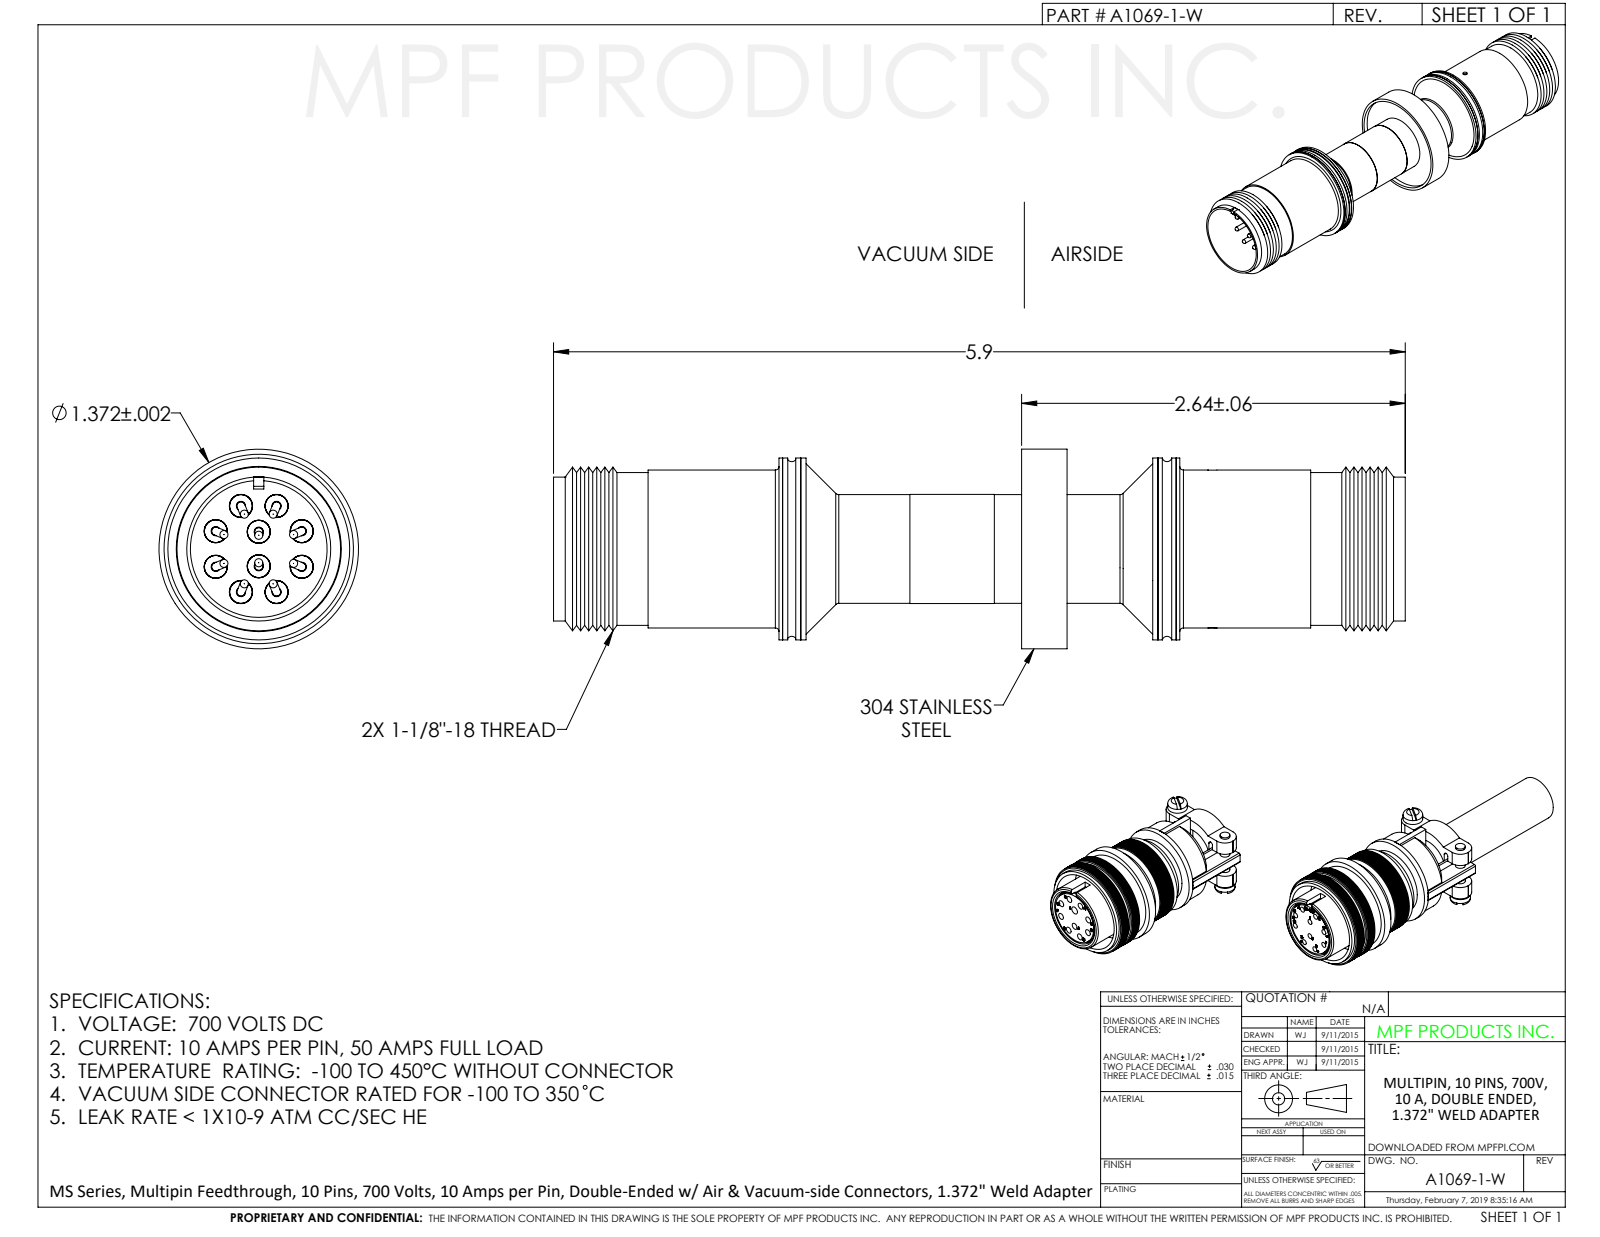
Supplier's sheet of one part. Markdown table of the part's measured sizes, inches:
| quantity | value |
| --- | --- |
| part name | A1069-1-W |
| STEP written by | SolidWorks 2012 (CONFIG_CONTROL_DESIGN) |
| units | inches |
| bodies | 1 solid, 695 faces (137 planar, 368 cylindrical, 190 other) |
| overall size | 5.855 × 1.372 × 1.372 |
| volume | 2.048 in³ |
| surface area | 65.12 in² |
| round holes (diameter × count) | 0.062 × 11, 0.159 × 10, 0.06 × 4, 0.625 × 1, 0.675 × 1, 0.682 × 1, 0.751 × 1, 0.94 × 1, 0.96 × 1, 0.97 × 1, 1.035 × 1, 1.302 × 1 |
| round bosses / shafts (diameter × count) | 0.056 × 48, 0.187 × 10, 0.171 × 10, 1.372 × 1, 1.25 × 1, 1.085 × 1, 1.05 × 1, 1.026 × 1 |
| partial cylindrical surfaces (radius × count) | 0.03 × 16 |
| main face-to-face distances | 0.252, 1.007, 0.755, 1.647, 1.395, 0.64, 0.04, 1.275, 2.133, 2.385 |
| hole center spacings | 0.229, 0.412, 0.535, 0.19, 0.061, 0.245, 0.259, 0.32 |
